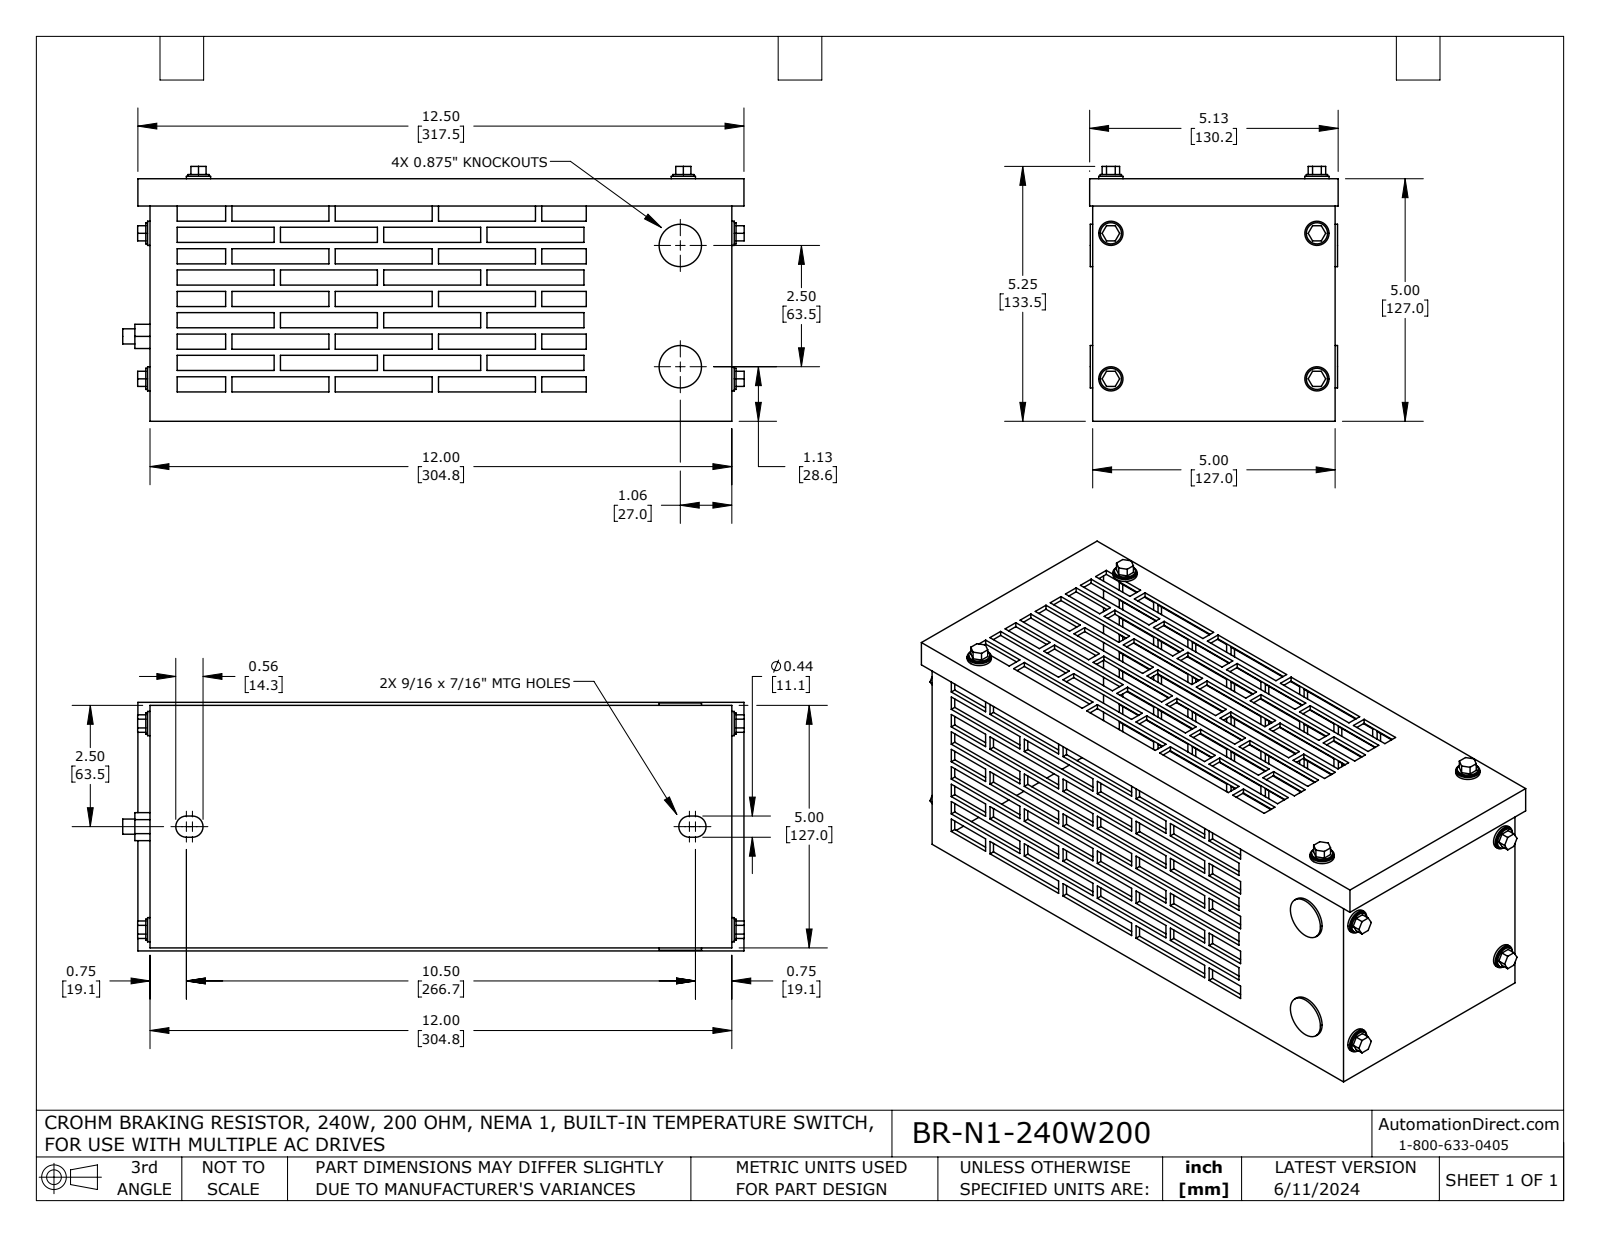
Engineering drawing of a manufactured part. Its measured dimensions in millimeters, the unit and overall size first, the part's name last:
Units: millimetres
Overall size (bounding box): 325.6 × 133.5 × 130.2
Round holes (diameter × count): ⌀6.4 ×8, ⌀19.1 ×2
Round bosses / shafts (diameter × count): ⌀12.7 ×8, ⌀11.1 ×8, ⌀22.2 ×2, ⌀8 ×1
Partial cylindrical surfaces — rounded edges, fillets, slot ends (radius × count): R5.6 ×4
Main face-to-face distances: 2.5, 124.5, 127, 121.9, 302.3, 1.6, 126.1, 304.8, 299.7, 22.4
Hole centre spacings: 108, 76.2, 132.1, 254, 276, 63.5
Volume: 370 300 mm³ · Surface area: 330 100 mm²
Bodies: 30 solids, 753 faces (659 planar, 94 cylindrical, 0 other)
Part name (STEP PRODUCT): BR-N1-240W200
STEP written by: SolidWorks 2021 (AUTOMOTIVE_DESIGN)
